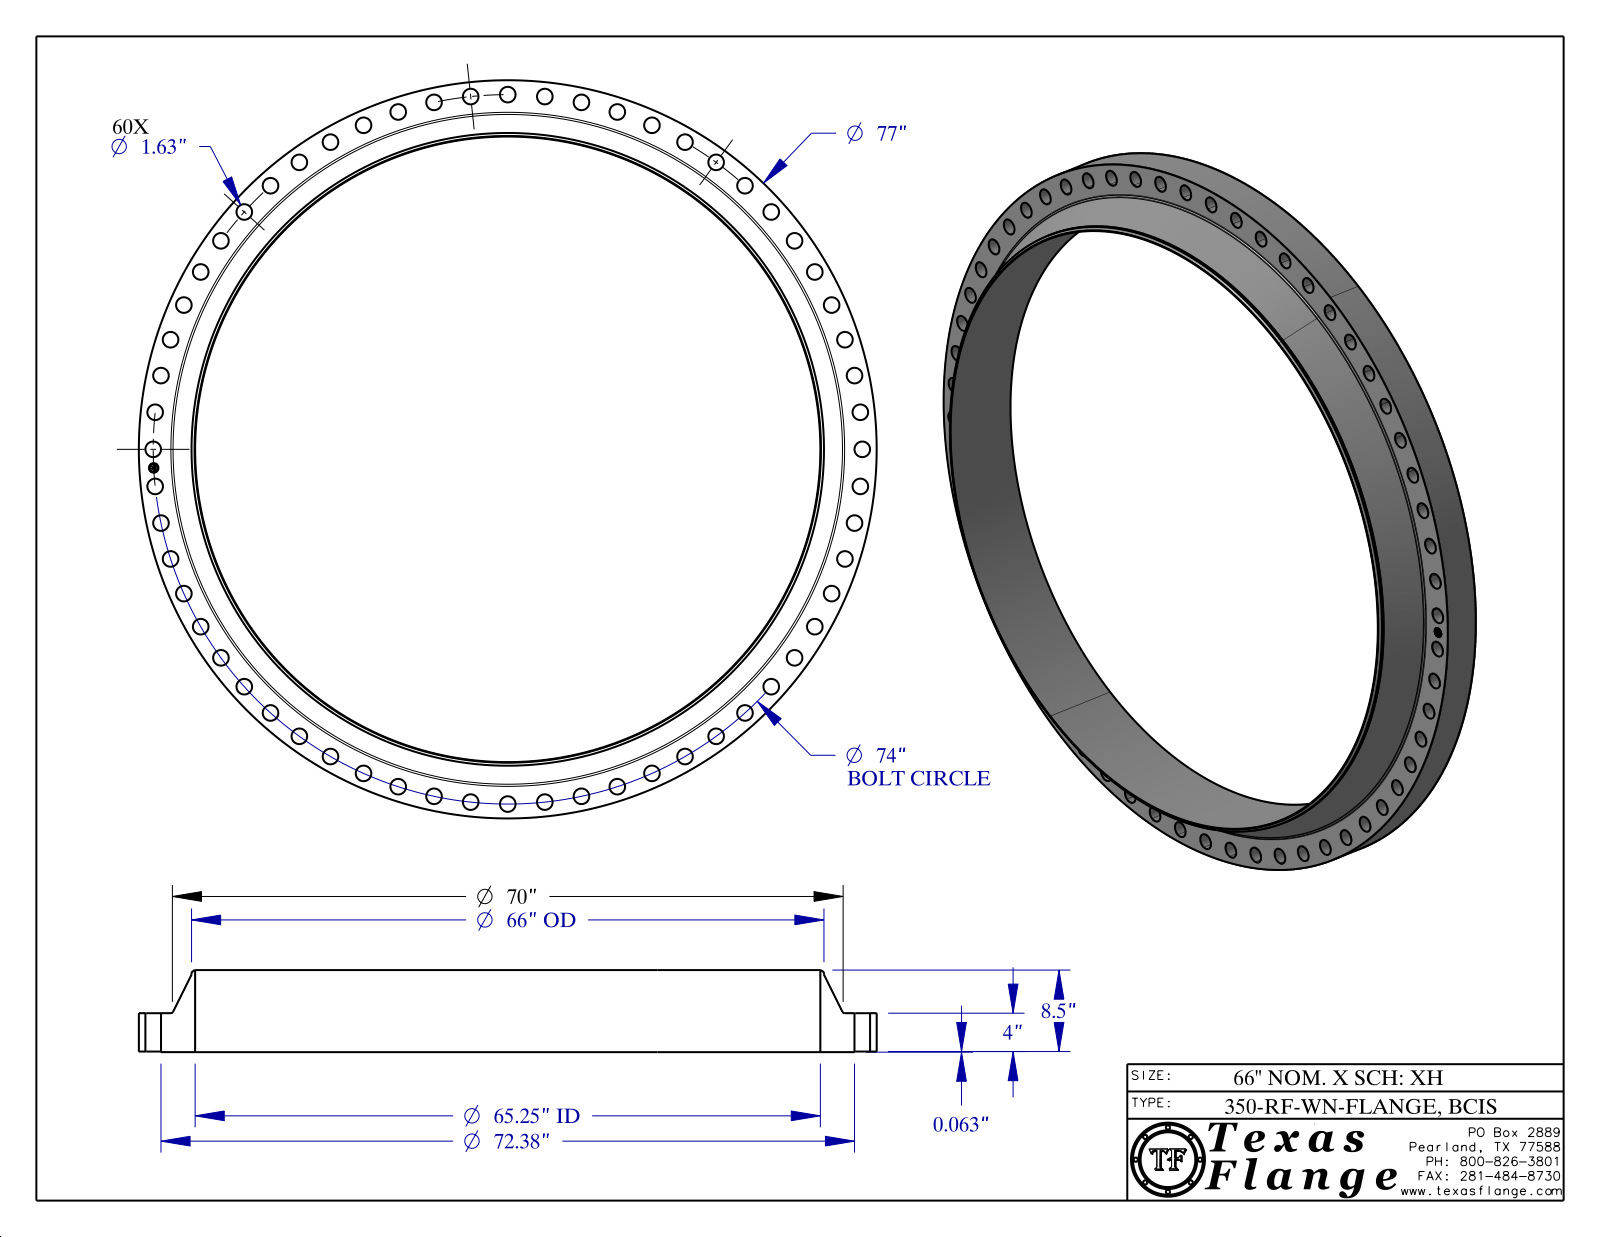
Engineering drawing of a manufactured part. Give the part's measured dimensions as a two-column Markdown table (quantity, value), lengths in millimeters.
| quantity | value |
| --- | --- |
| part name | 350-RF-WN, BCIS |
| STEP written by | CATIA V5 STEP AP214 (AUTOMOTIVE_DESIGN) |
| units | millimeters |
| bodies | 1 solid, 583 faces (369 planar, 208 cylindrical, 6 other) |
| overall size | 1955.8 × 1955.8 × 217.5 |
| volume | 98 170 000 mm³ |
| surface area | 4 473 000 mm² |
| round holes (diameter × count) | 41.4 × 60, 25.4 × 1, 1657.4 × 1 |
| round bosses / shafts (diameter × count) | 1.5 × 8, 1955.8 × 1, 1838.5 × 1, 1676.4 × 1, 20 × 1 |
| main face-to-face distances | 103.2, 1.6, 101.6, 217.5, 215.9, 114.3, 102.8, 101.2, 0.4, 114.7 |
| hole center spacings | 939.8, 390.8, 98.4, 196.5, 853.3, 1877, 580.8, 1869.3 |
